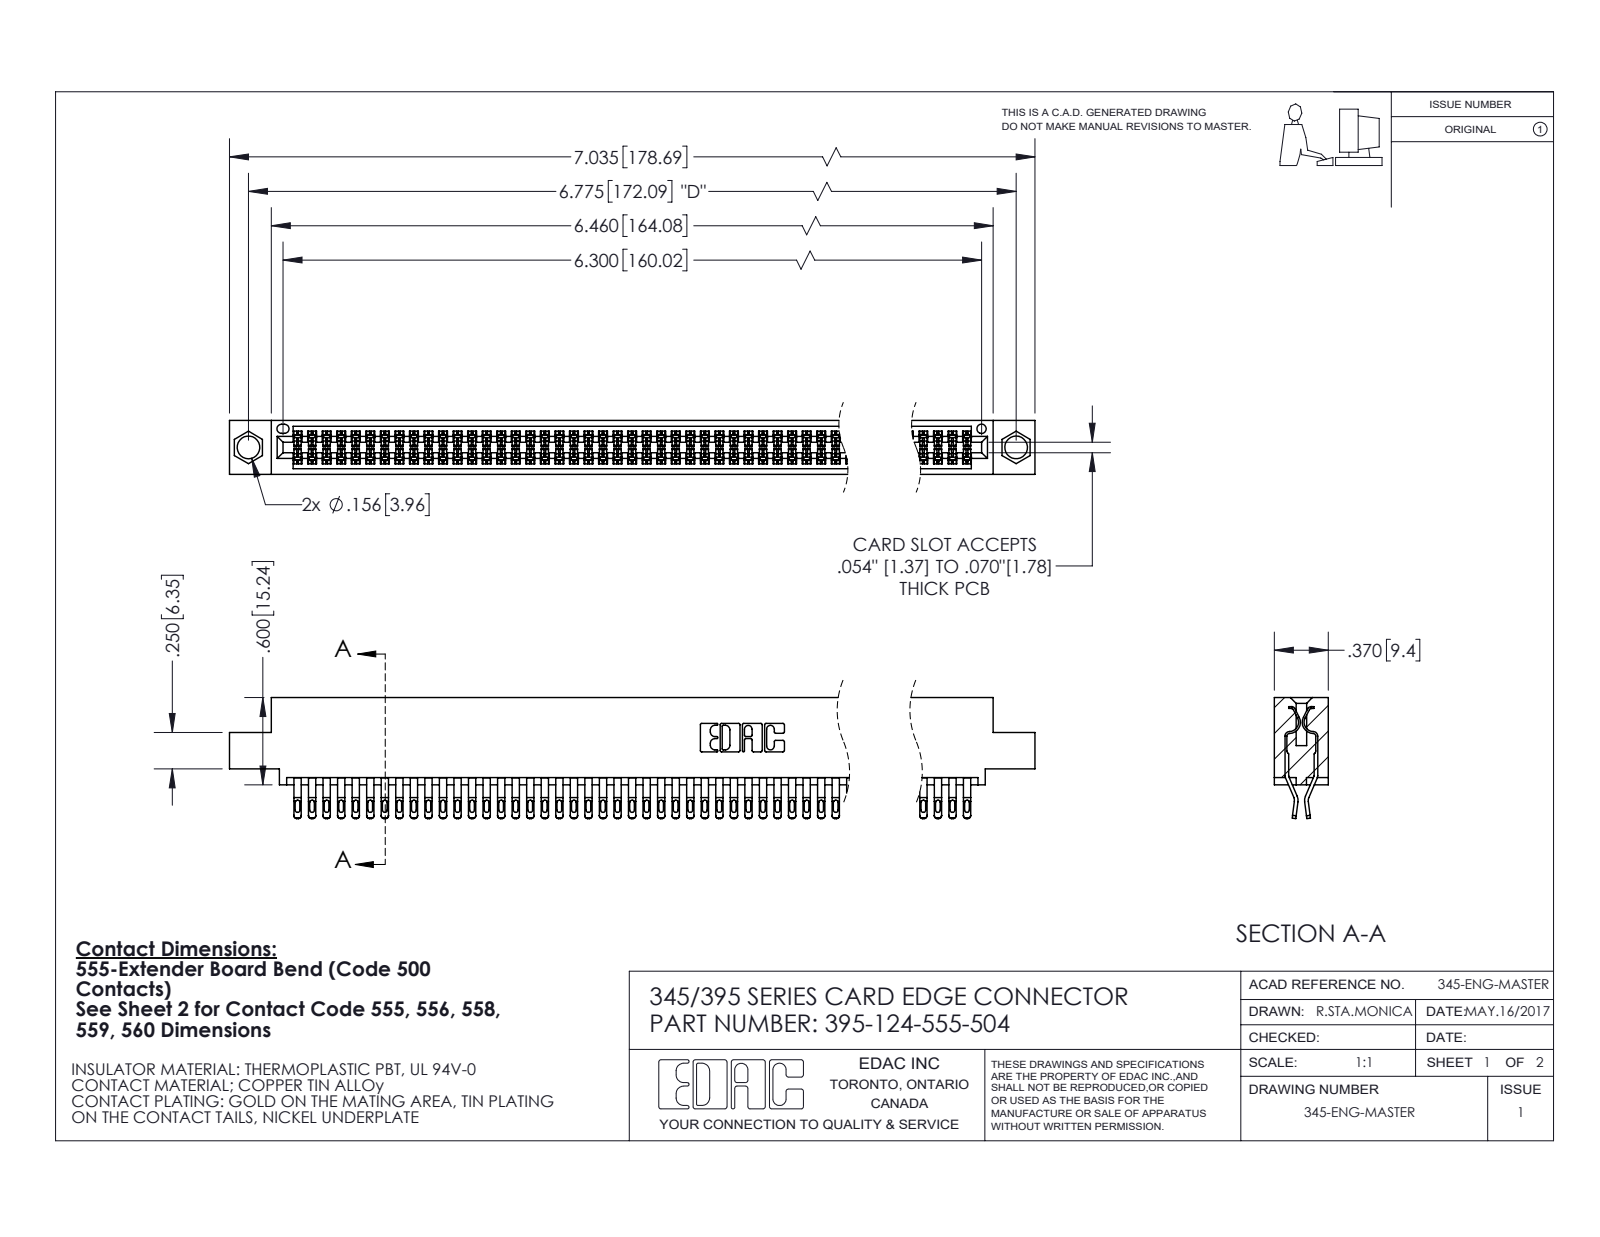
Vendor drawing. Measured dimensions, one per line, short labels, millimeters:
name: 395-124-555-504; 345 Part_0.110 Offset - 0.156 Dia-TI; 345-292-001_555 Tail
written by: SolidWorks 2020 (CONFIG_CONTROL_DESIGN)
unit: mm
bodies: 125 solids, 7088 faces (3942 planar, 3146 cylindrical, 0 other)
size: 178.7 × 21.1 × 9.4
volume: 17 730 mm³; area: 27 780 mm²
holes: 2× ⌀4, 1× ⌀1.6
rounds: 310× R0.4, 248× R0.2, 248× R0.5, 22× R0.3, 6× R0.2, 6× R0.8, 3× R0.7, 2× R0.3
face distances: 7.6, 1.8, 0.6, 9.4, 5.1, 2.5, 6.9, 5.7, 4.4, 3.8
hole spacings: 6.9, 166.1, 172.1
